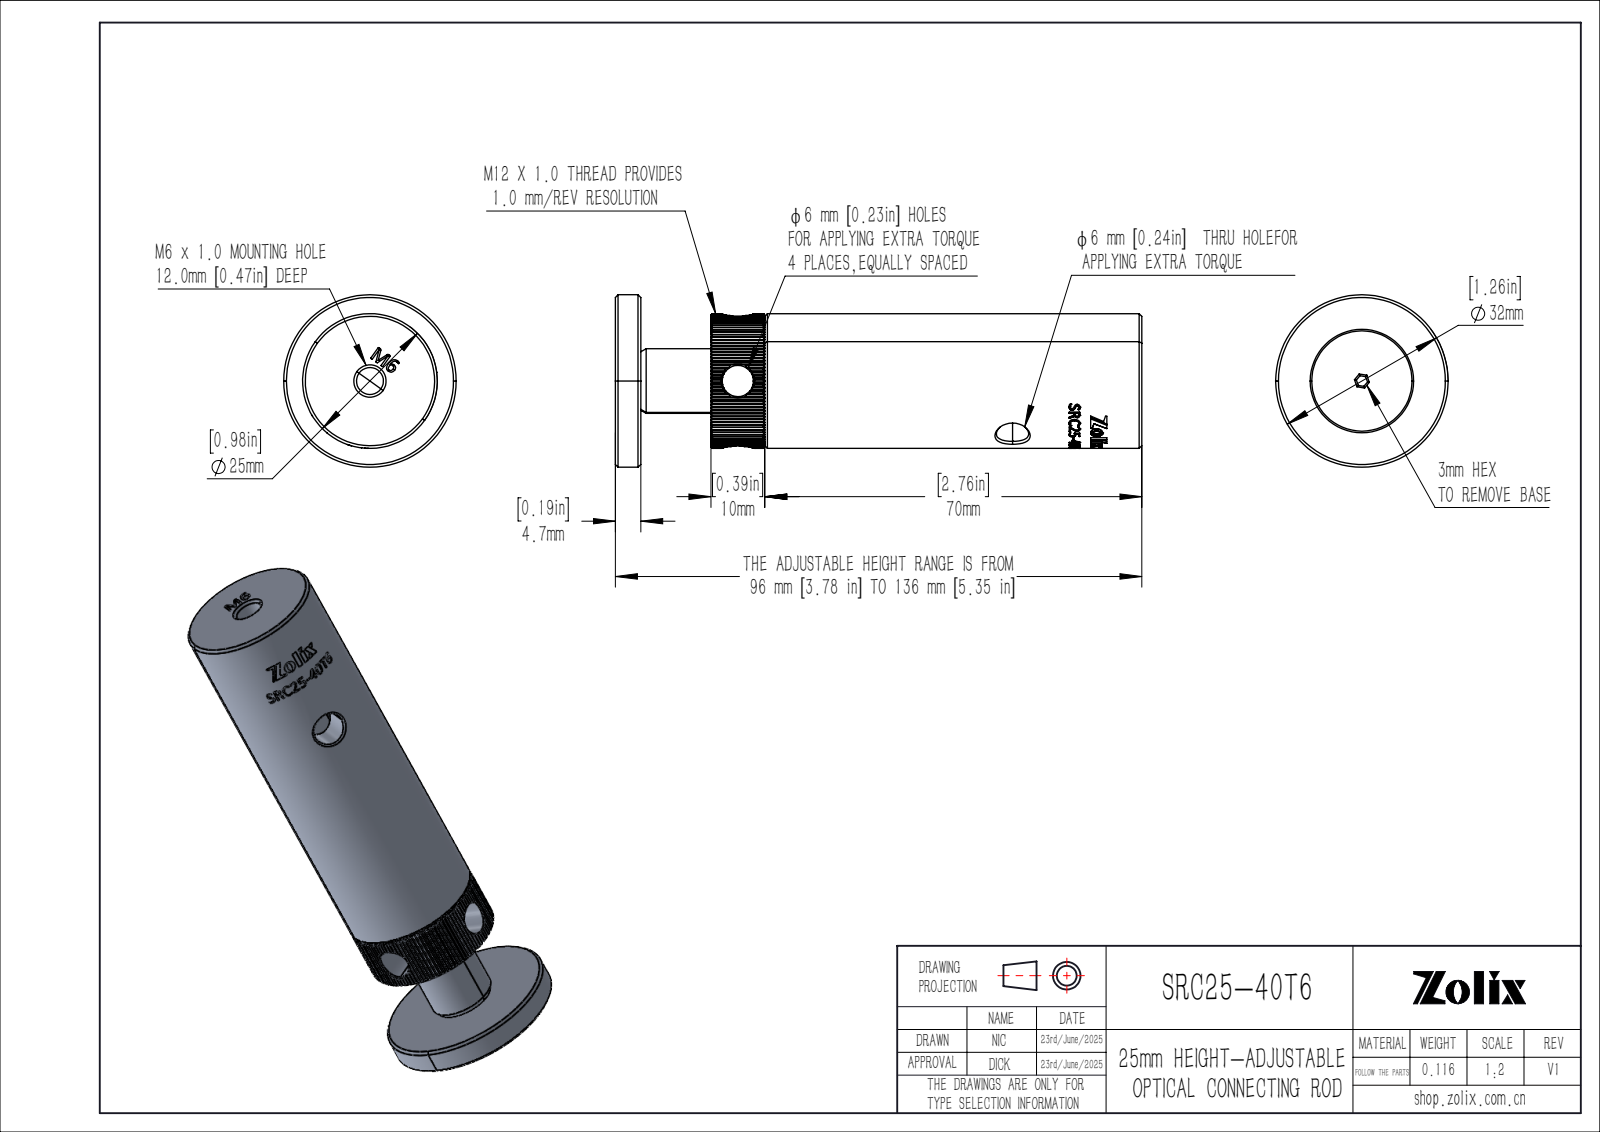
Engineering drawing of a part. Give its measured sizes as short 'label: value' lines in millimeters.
name: SRC25-40T6
written by: SolidWorks 2020 (CONFIG_CONTROL_DESIGN)
unit: mm
bodies: 4 solids, 1239 faces (408 planar, 219 cylindrical, 612 other)
size: 97.72 × 32 × 32
volume: 42 846 mm³; area: 16 602 mm²
holes: 2× ⌀5.8, 1× ⌀0.8, 1× ⌀3.3, 1× ⌀5, 1× ⌀6, 1× ⌀11, 1× ⌀12, 1× ⌀12.2
bosses: 1× ⌀32, 1× ⌀25, 1× ⌀6, 1× ⌀5.2
rounds: 1× R12.48
face distances: 23.02, 27.72, 4.7, 70, 17.72, 93.02, 97.72, 80, 10, 13.02
